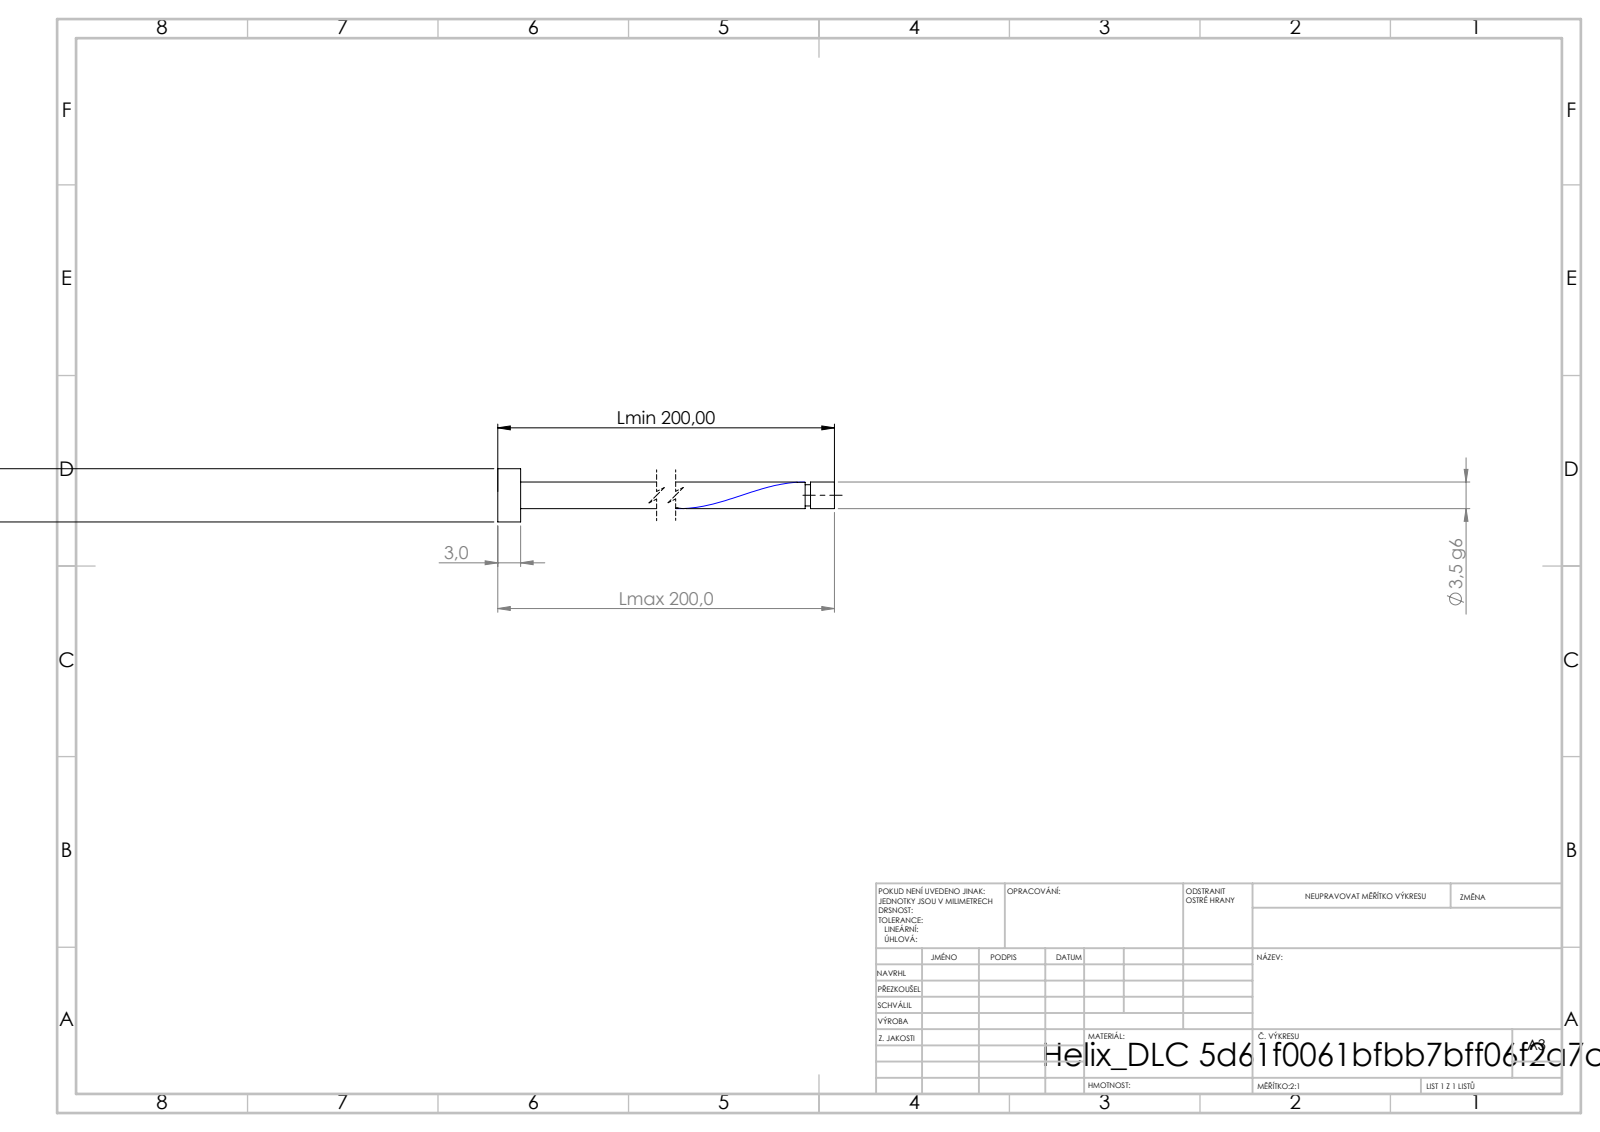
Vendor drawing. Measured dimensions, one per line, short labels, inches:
written by: SolidWorks 2019 (CONFIG_CONTROL_DESIGN)
unit: in
bodies: 1 solid, 16 faces (6 planar, 9 cylindrical, 1 other)
size: 7.874 × 0.276 × 0.276
volume: 0.148 in³; area: 4.779 in²
bosses: 1× ⌀0.276, 1× ⌀0.138, 1× ⌀0.11
face distances: 0.118, 7.874, 7.756, 7.75, 7.632, 0.124, 7.722, 7.604, 0.028, 0.152
